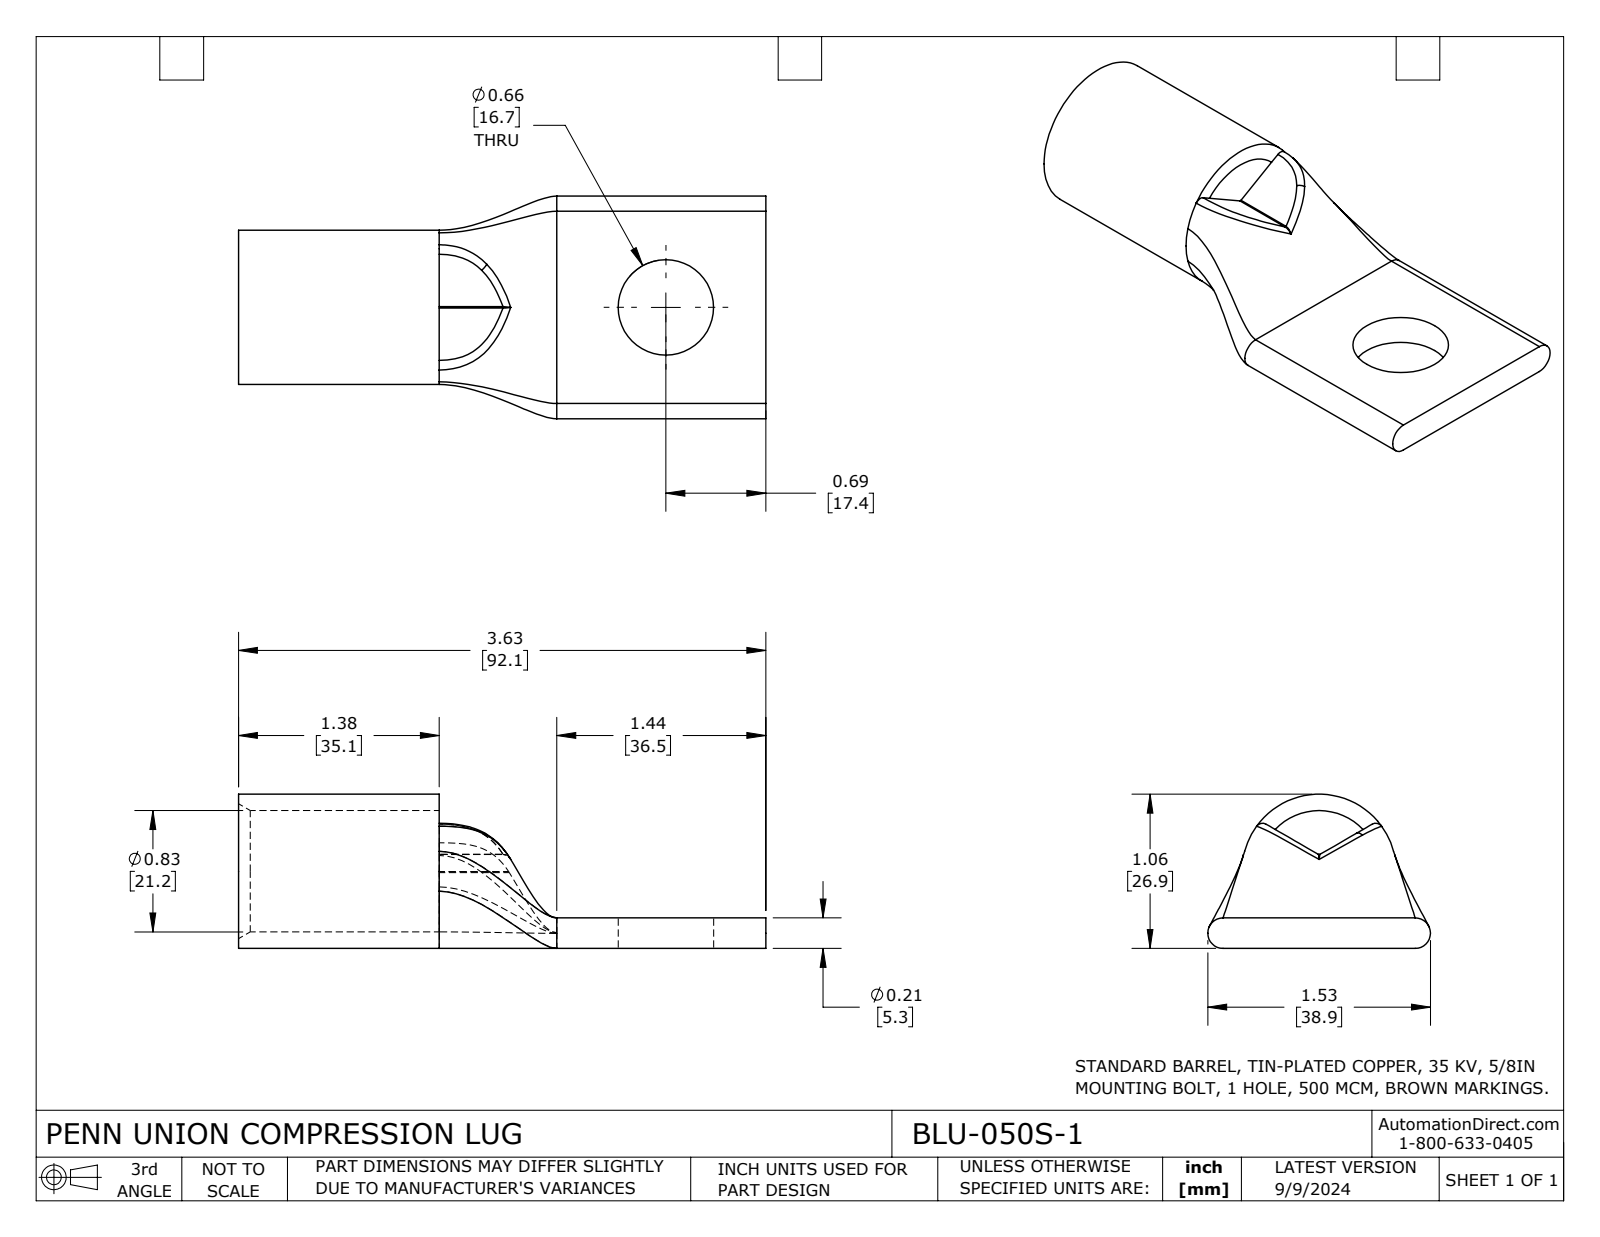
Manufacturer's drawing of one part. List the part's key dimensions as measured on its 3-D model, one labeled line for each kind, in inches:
Part name (STEP PRODUCT): BLU-050S-1
STEP written by: SolidWorks 2023 (CONFIG_CONTROL_DESIGN)
Units: inches
Bodies: 1 solid, 36 faces (11 planar, 11 cylindrical, 14 other)
Overall size (bounding box): 3.625 × 1.531 × 1.06
Volume: 1.081 in³ · Surface area: 18.75 in²
Round holes (diameter × count): ⌀0.656 ×1, ⌀0.834 ×1
Round bosses / shafts (diameter × count): ⌀1.06 ×1
Partial cylindrical surfaces — rounded edges, fillets, slot ends (radius × count): R0.105 ×2, R0.01 ×1, R0.05 ×1
Main face-to-face distances: 0.21, 0.113, 3.625, 1.38, 2.245, 2.188, 0.808, 1.437
